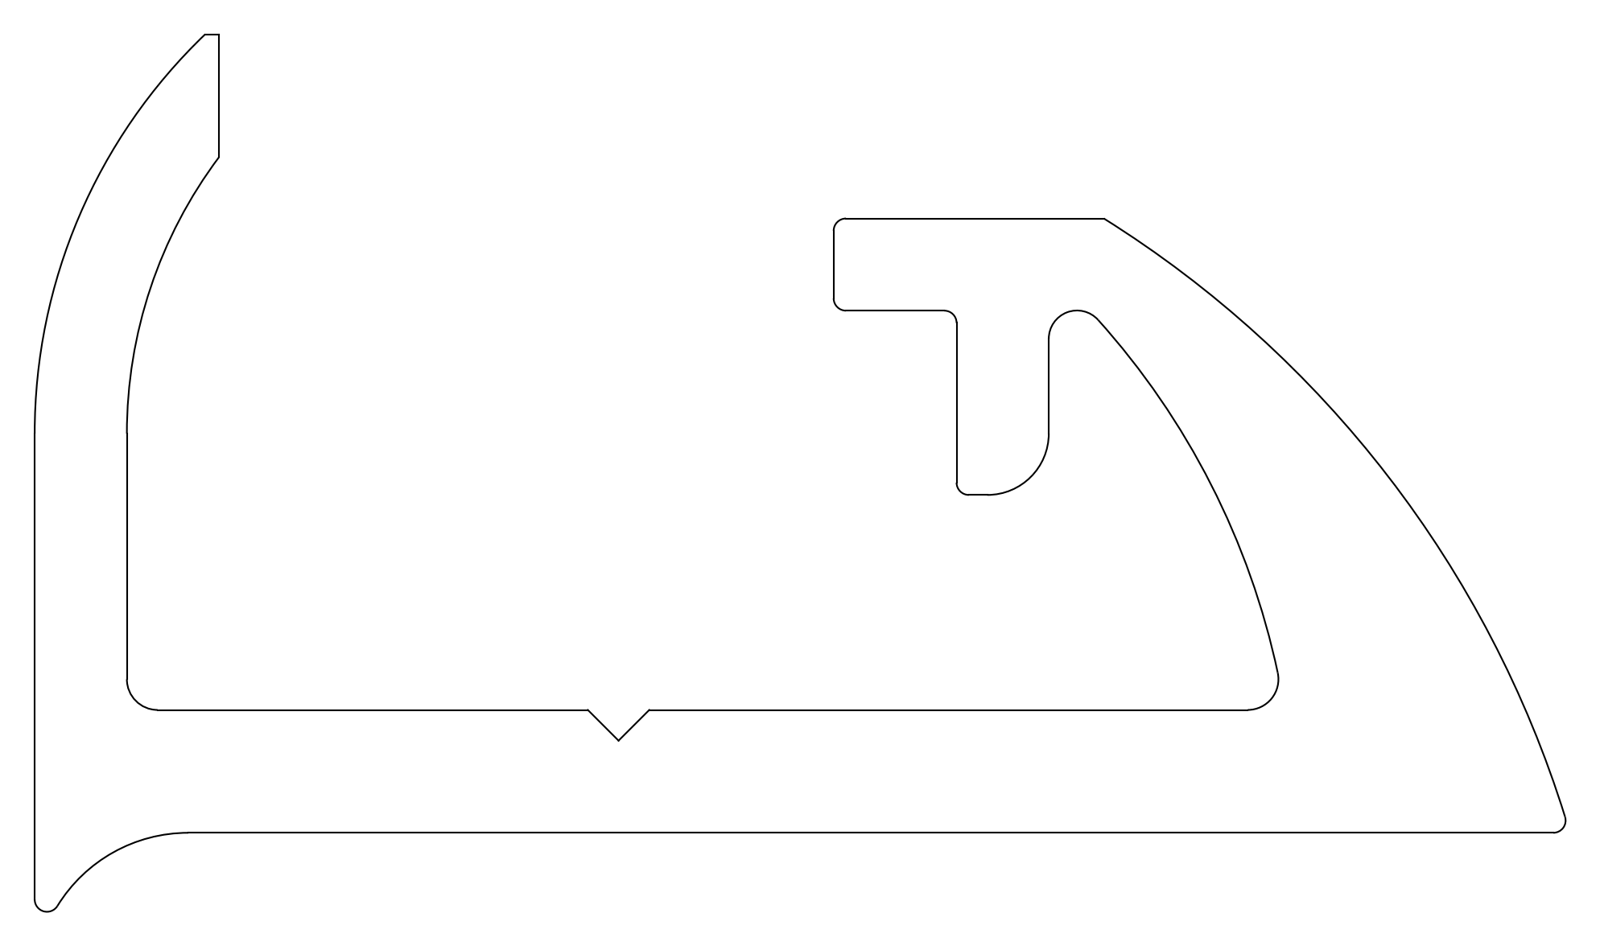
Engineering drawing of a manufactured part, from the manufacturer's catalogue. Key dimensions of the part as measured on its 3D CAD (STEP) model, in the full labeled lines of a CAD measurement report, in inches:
STEP written by: THINKDESIGN (CONFIG_CONTROL_DESIGN)
Units: inches
Bodies: 1 solid, 32 faces (17 planar, 15 cylindrical, 0 other)
Overall size (bounding box): 3.937 × 0.981 × 0.563
Volume: 0.604 in³ · Surface area: 16.7 in²
Partial cylindrical surfaces — rounded edges, fillets, slot ends (radius × count): R0.008 ×6, R0.02 ×2, R0.018 ×1, R0.039 ×1, R0.098 ×1, R0.295 ×1, R0.354 ×1, R0.492 ×1
Main face-to-face distances: 0.079, 0.059, 0.394, 0.315, 0.591, 0.531, 0.118, 0.472, 0.335, 0.256
